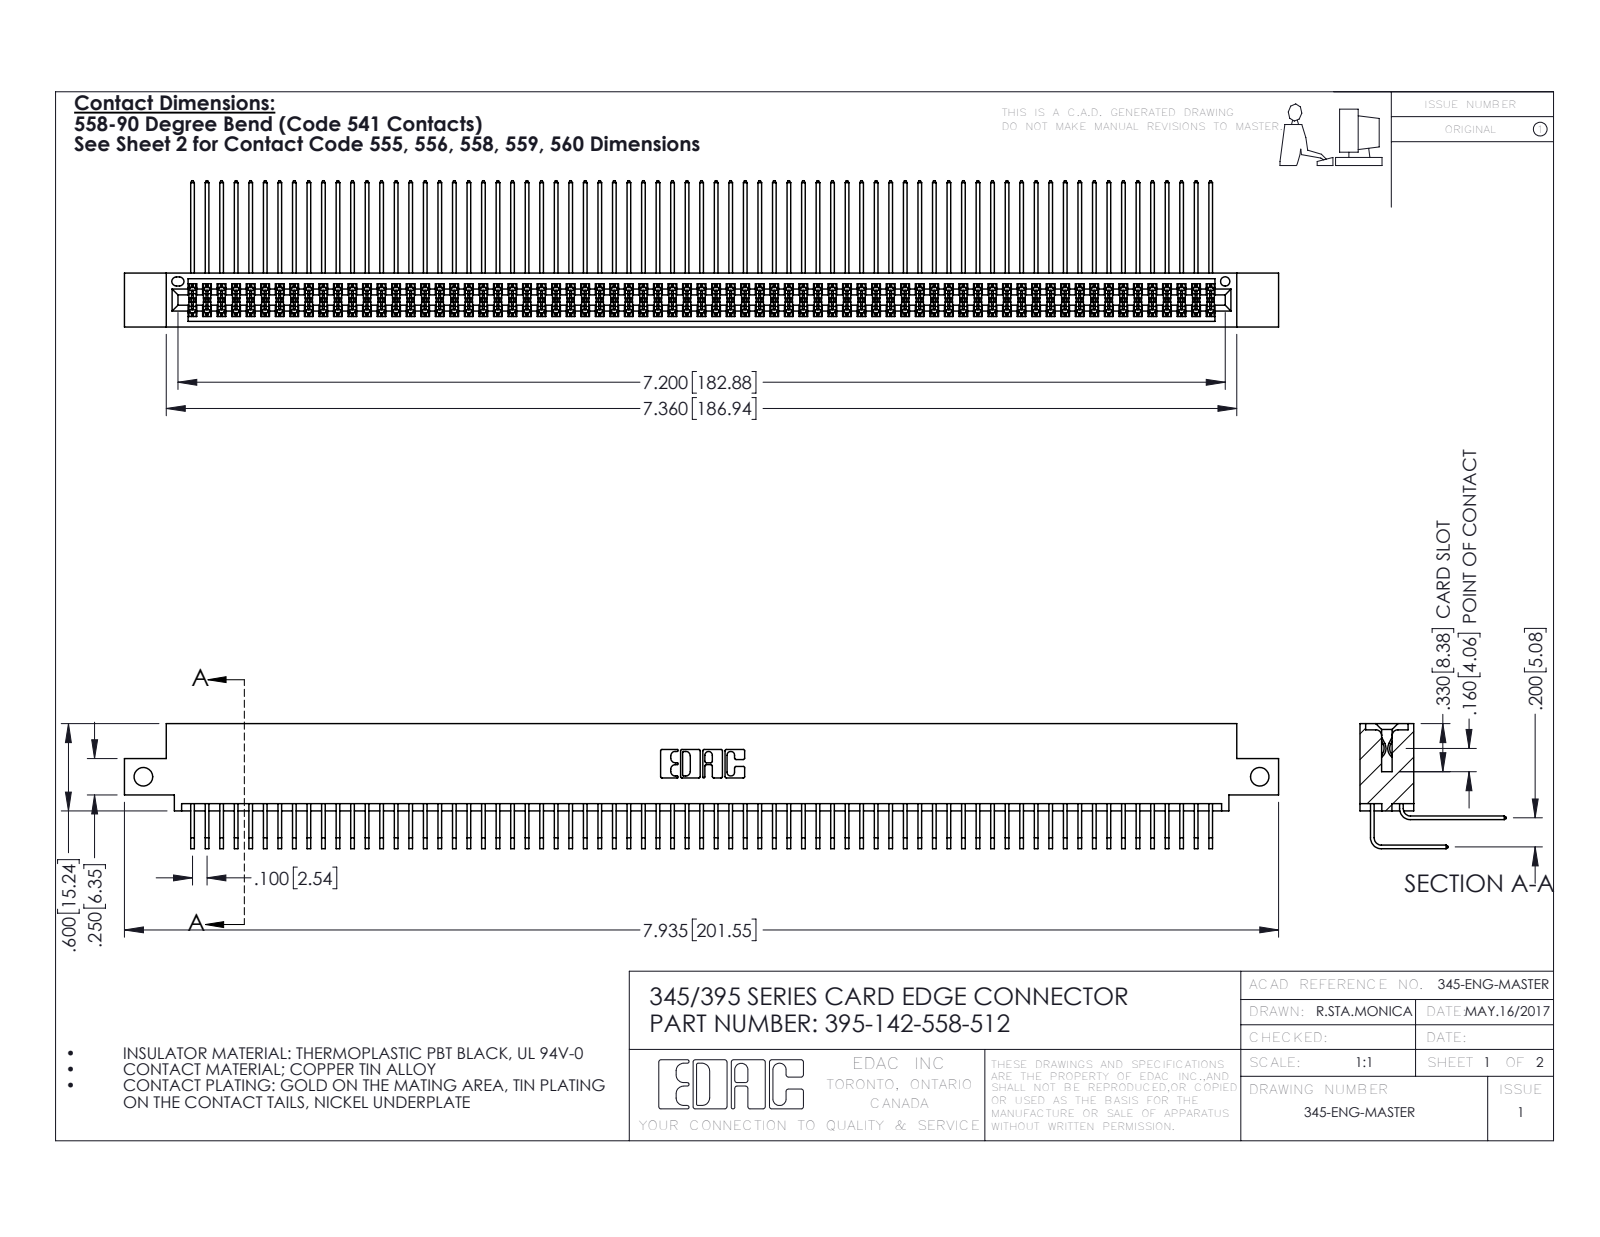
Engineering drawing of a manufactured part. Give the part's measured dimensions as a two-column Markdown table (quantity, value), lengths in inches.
| quantity | value |
| --- | --- |
| part name | 345-292-001_558 559 Tail - 1; 345 Part_0.110 Offset - Side Mount; 345-292-001_558 Tail - 2; 395-142-558-512 |
| STEP written by | SolidWorks 2016 (CONFIG_CONTROL_DESIGN) |
| units | inches |
| bodies | 143 solids, 7514 faces (5054 planar, 2460 cylindrical, 0 other) |
| overall size | 7.935 × 1.005 × 0.859 |
| volume | 1.251 in³ |
| surface area | 53.76 in² |
| round holes (diameter × count) | 0.128 × 2, 0.064 × 1 |
| partial cylindrical surfaces (radius × count) | 0.006 × 283, 0.01 × 22, 0.007 × 6, 0.031 × 6, 0.026 × 3, 0.014 × 2, 0.019 × 2, 0.022 × 2 |
| main face-to-face distances | 0.072, 0.298, 0.2, 0.37, 0.098, 0.272, 0.025, 0.225, 0.025, 0.175 |
| hole center spacings | 7.675 |
